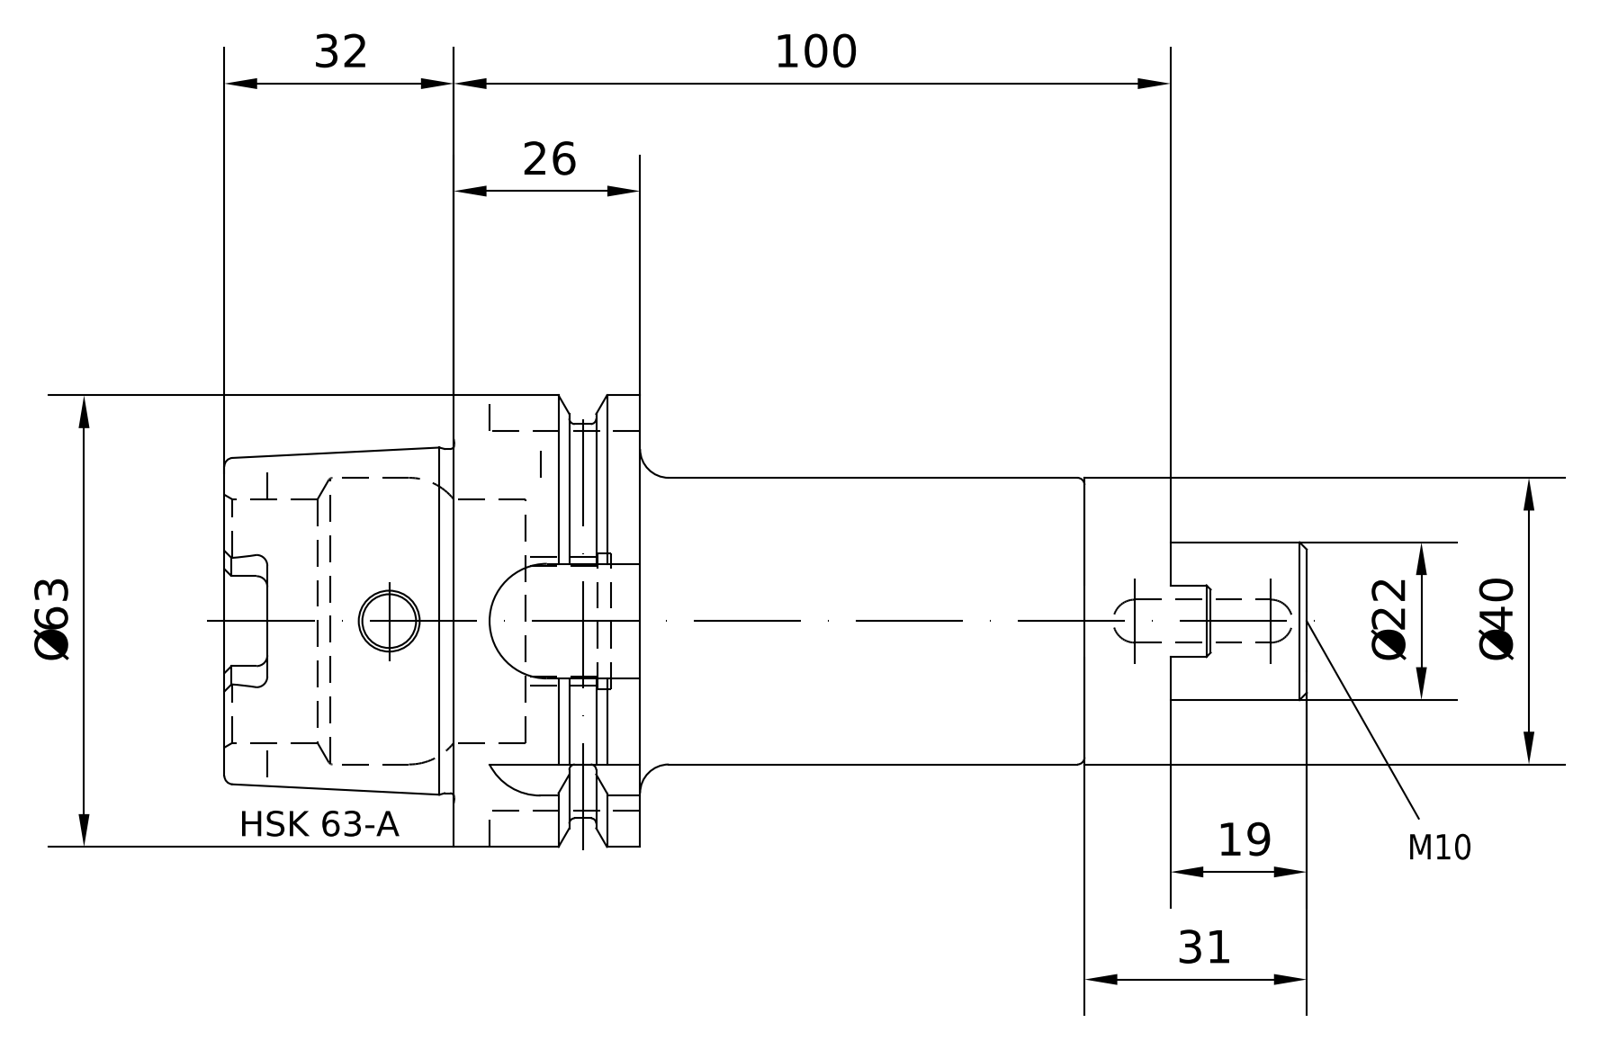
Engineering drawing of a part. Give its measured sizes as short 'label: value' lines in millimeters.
name: A63-041-22; 85-200-22; A63-041-22_ASM
written by: PRO/ENGINEER BY PARAMETRIC TECHNOLOGY CORPORATION, 2010430 (CONFIG_CONTROL_DESIGN)
unit: mm
bodies: 2 solids, 265 faces (123 planar, 64 cylindrical, 78 other)
size: 151 × 63 × 63
volume: 178 157 mm³; area: 39 740 mm²
holes: 2× ⌀10, 1× ⌀7.5, 1× ⌀8.5, 1× ⌀16.92, 1× ⌀18.32, 1× ⌀18.66, 1× ⌀22.36, 1× ⌀26, 1× ⌀34
bosses: 1× ⌀63, 1× ⌀55, 1× ⌀48.04, 1× ⌀40, 1× ⌀22, 1× ⌀18
rounds: 6× R1.5, 6× R3, 1× R5.05, 1× R8, 1× R8.02, 1× R9.02
face distances: 88, 26, 62, 10, 100, 74, 12, 16, 78, 90
